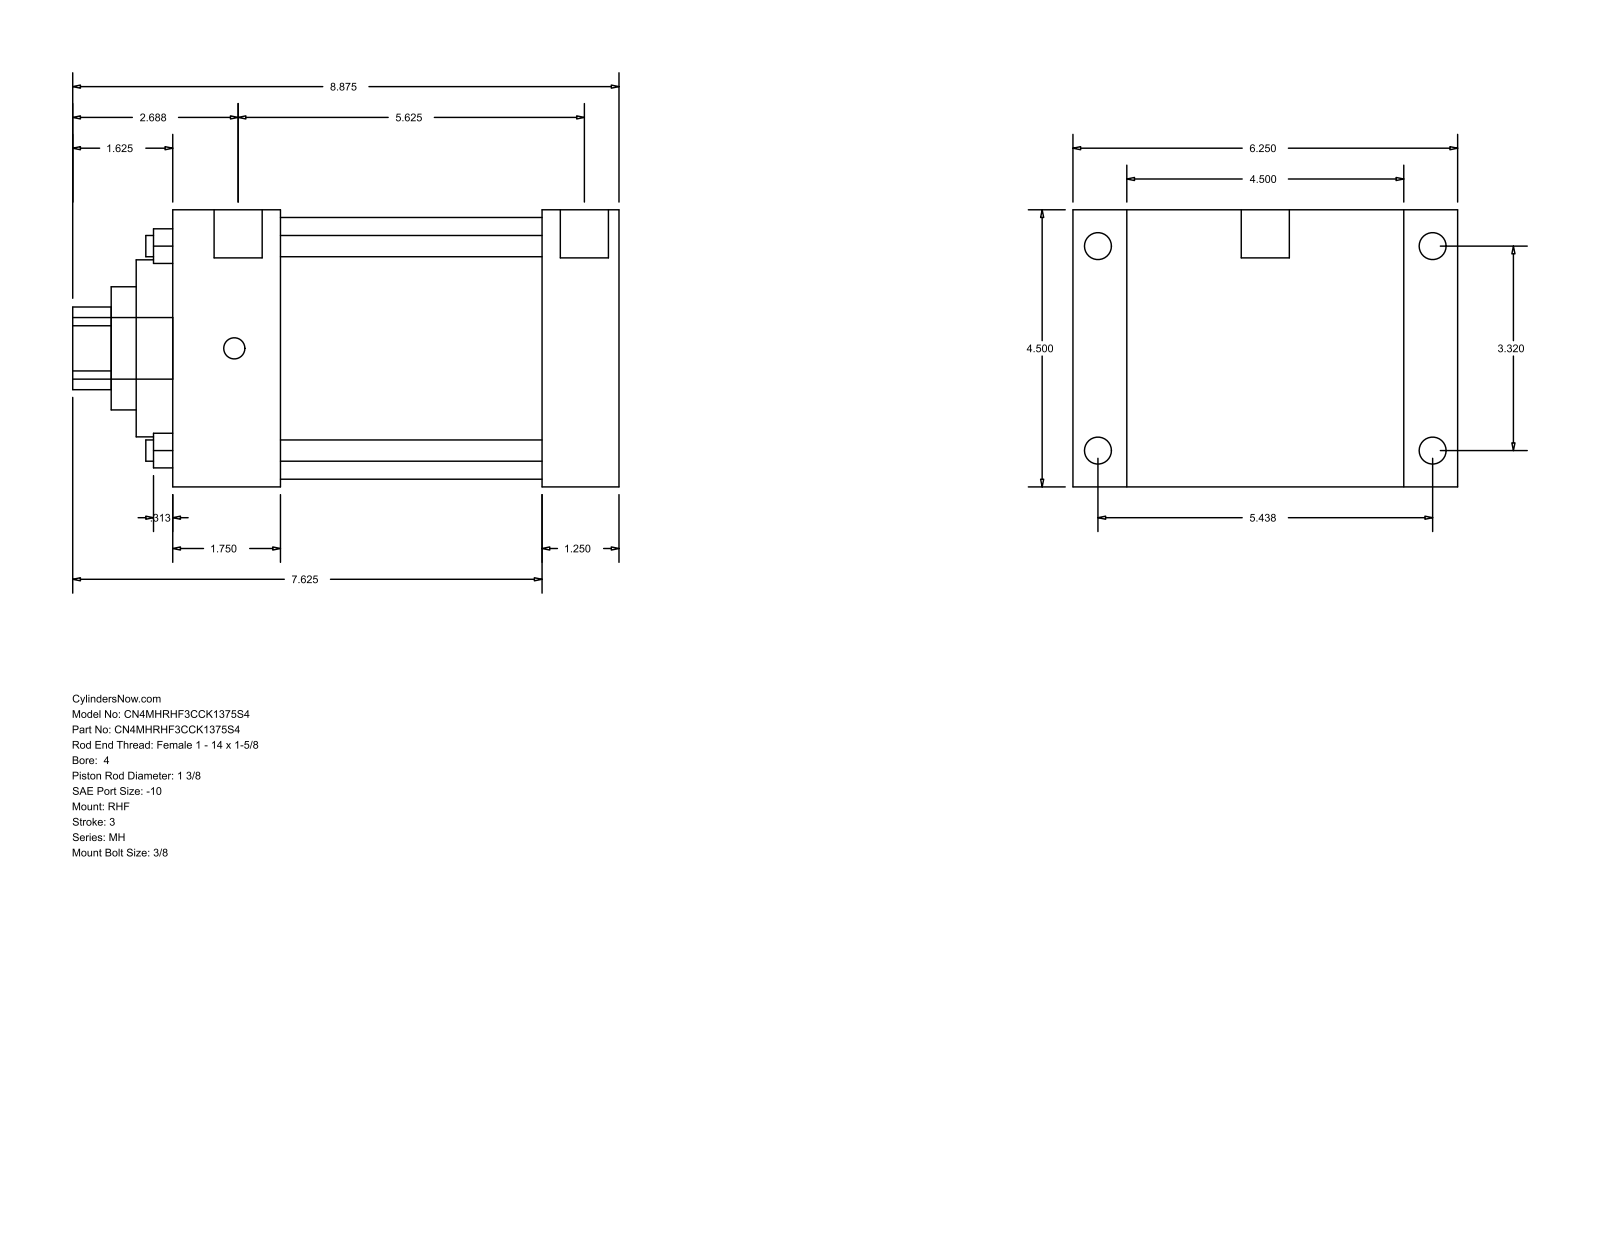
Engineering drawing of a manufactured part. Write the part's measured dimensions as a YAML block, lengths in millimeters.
part_name: "MH_RHF__0400_1.375"
step_written_by: "GSSL Pune (CONFIG_CONTROL_DESIGN)"
units: millimeters
bodies: {solids: 0, faces: 90, planar: 61, cylindrical: 29, other: 0}
overall_size: [225.43, 158.75, 114.3]
round_holes:
  - {diameter: 8.76, count: 4}
  - {diameter: 34.92, count: 1}
  - {diameter: 50.8, count: 1}
  - {diameter: 73.03, count: 1}
  - {diameter: 107.95, count: 1}
round_bosses_or_shafts:
  - {diameter: 11.13, count: 4}
  - {diameter: 8.73, count: 4}
  - {diameter: 19.84, count: 2}
  - {diameter: 25.4, count: 1}
partial_cylinders:
  - {radius: 17.06, count: 1}
face_to_face_distances: [114.3, 184.16, 152.41, 31.75, 22.23, 136.53, 44.45, 107.96, 139.71, 158.76]
hole_center_spacings: [59.62, 84.32, 119.25]
